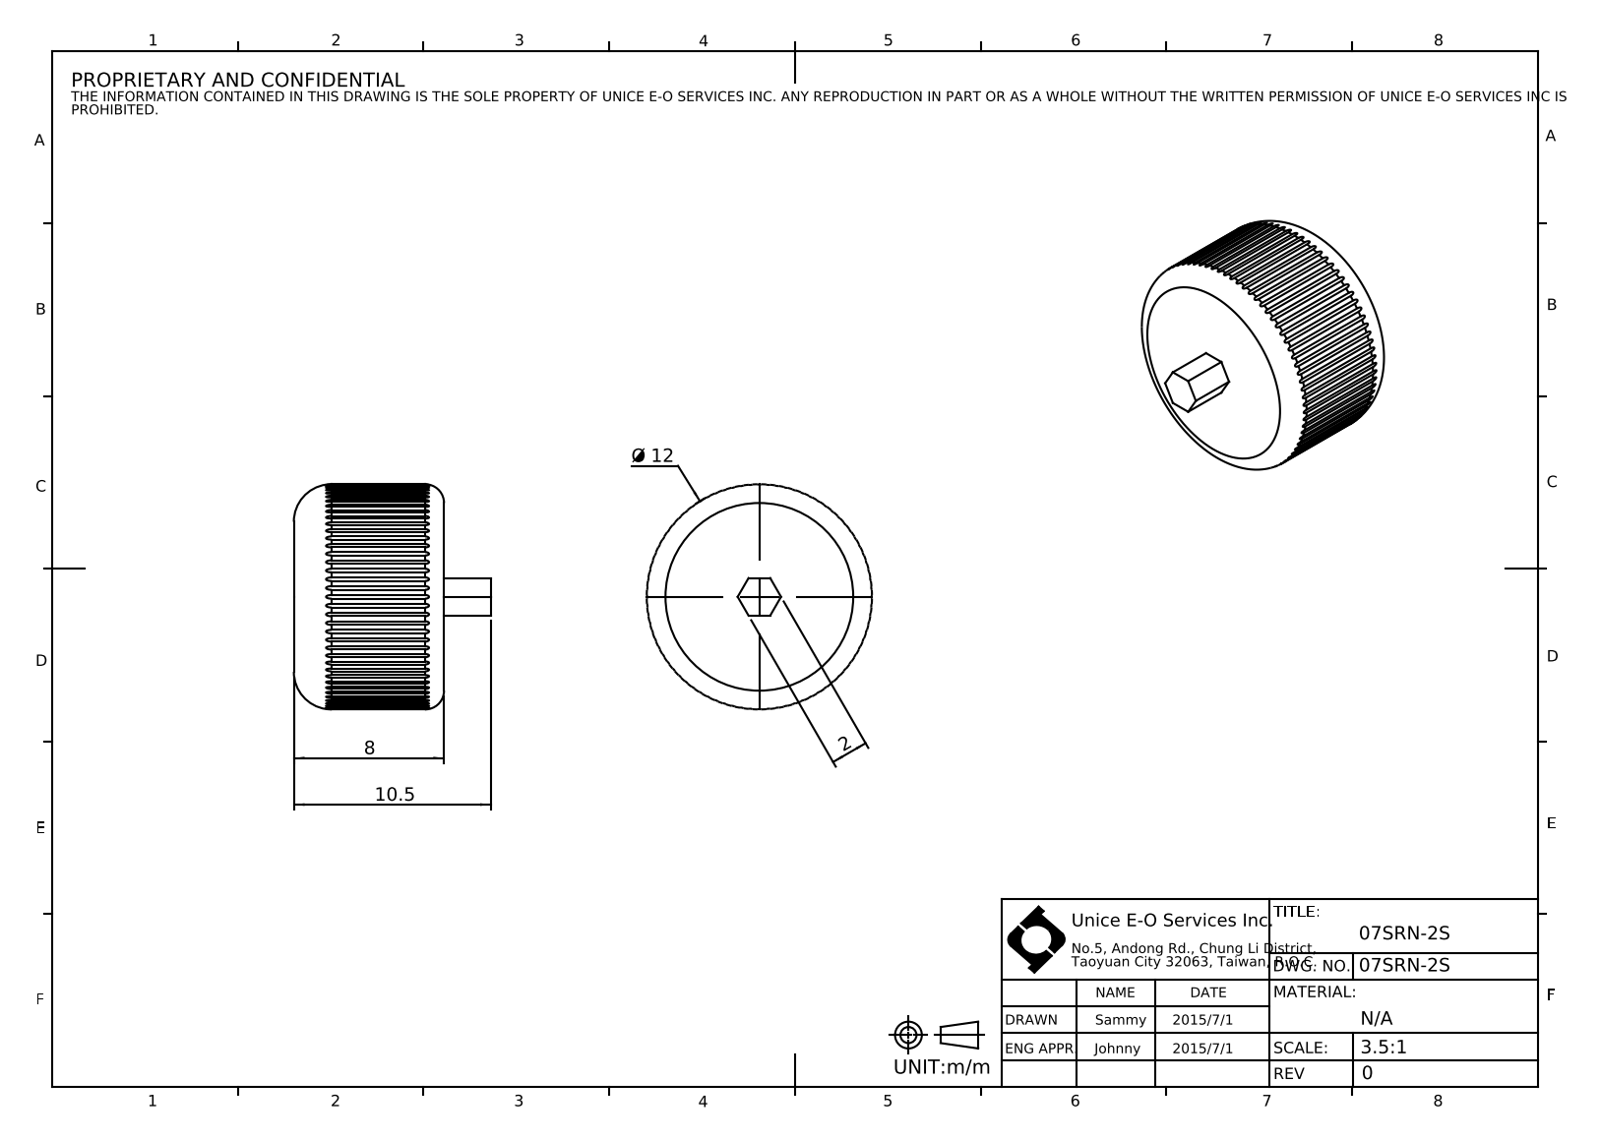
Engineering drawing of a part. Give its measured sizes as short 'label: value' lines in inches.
name: 07SRN-2S
written by: SolidWorks 2016 (CONFIG_CONTROL_DESIGN)
unit: in
bodies: 1 solid, 173 faces (9 planar, 160 cylindrical, 4 other)
size: 0.472 × 0.472 × 0.413
volume: 0.053 in³; area: 0.769 in²
rounds: 80× R0.01, 1× R0.236
face distances: 0.315, 0.079, 0.098, 0.413
